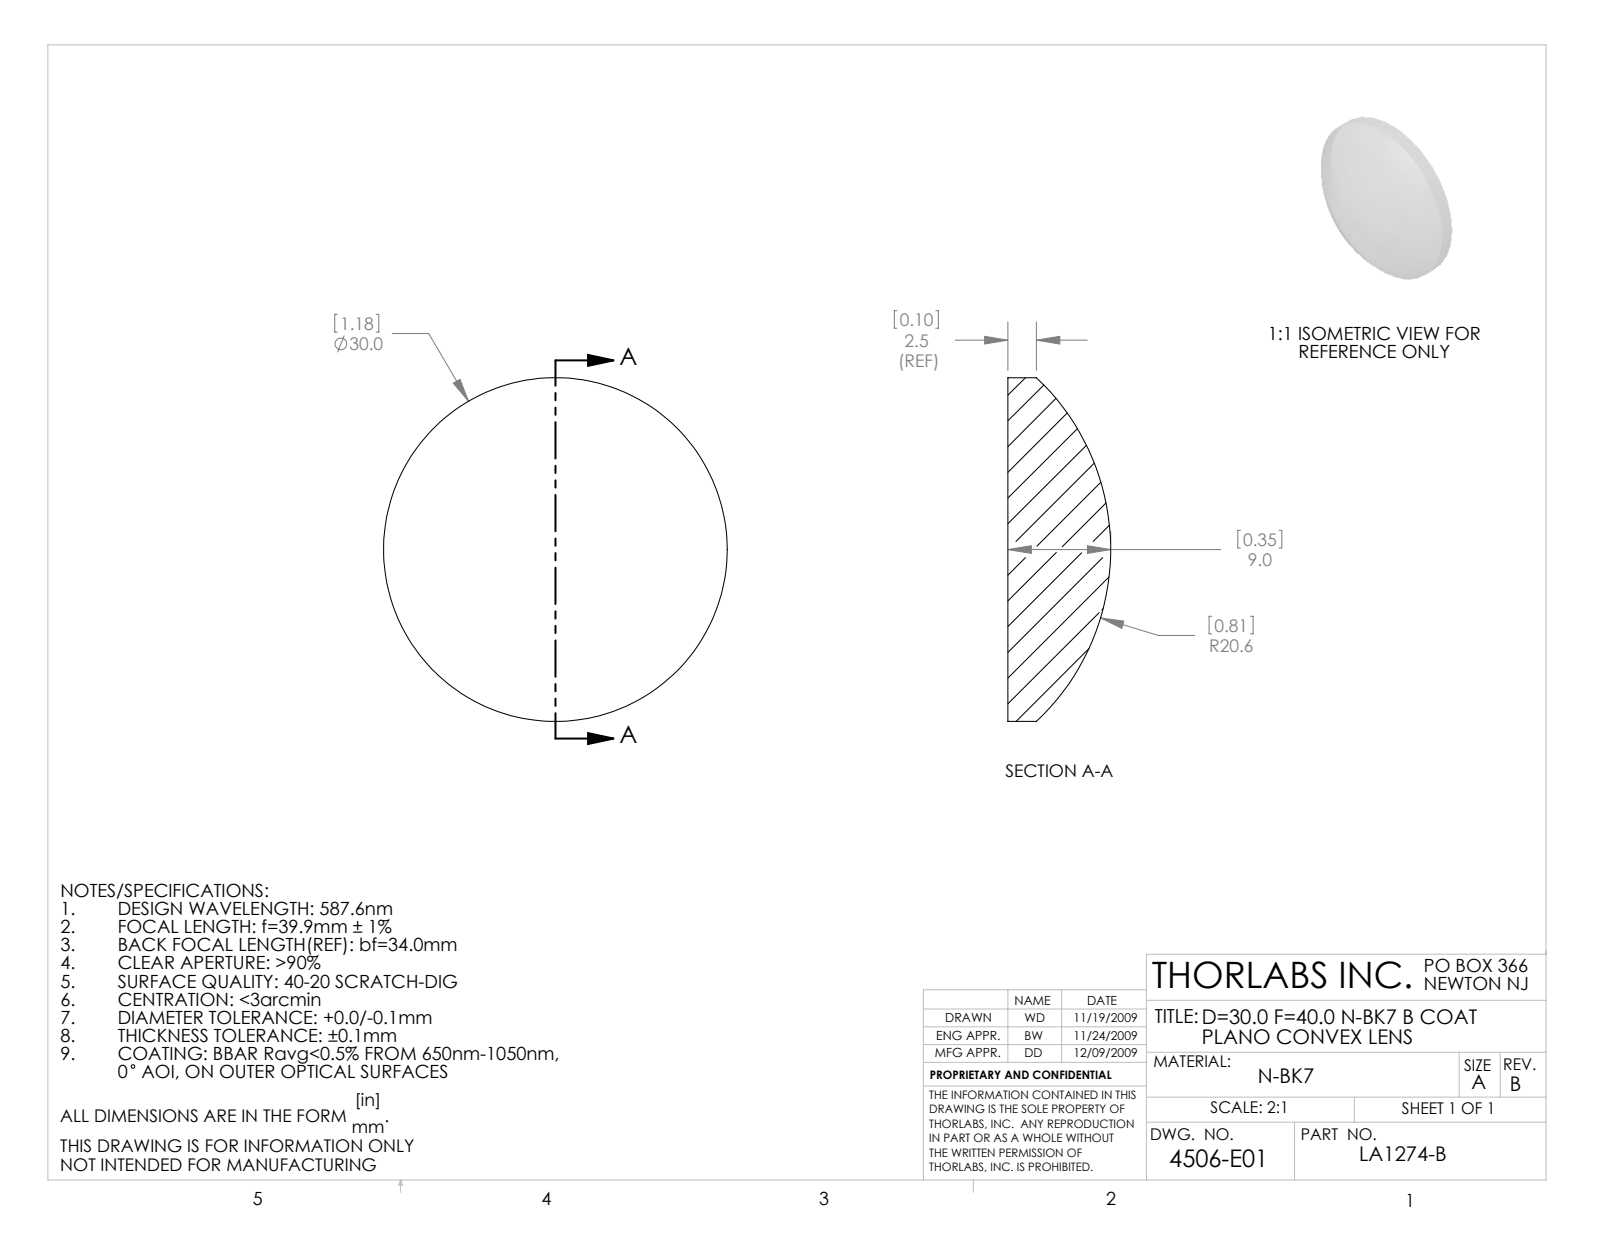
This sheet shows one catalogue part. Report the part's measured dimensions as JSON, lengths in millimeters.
{"part_name": "4506-E0W", "step_written_by": "SolidWorks 2009 (AUTOMOTIVE_DESIGN)", "units": "millimeters", "bodies": {"solids": 1, "faces": 5, "planar": 1, "cylindrical": 2, "other": 2}, "overall_size": [30, 30, 8.97], "volume_mm3": 4193, "surface_area_mm2": 1780, "round_bosses_or_shafts": [[30, 1]]}
